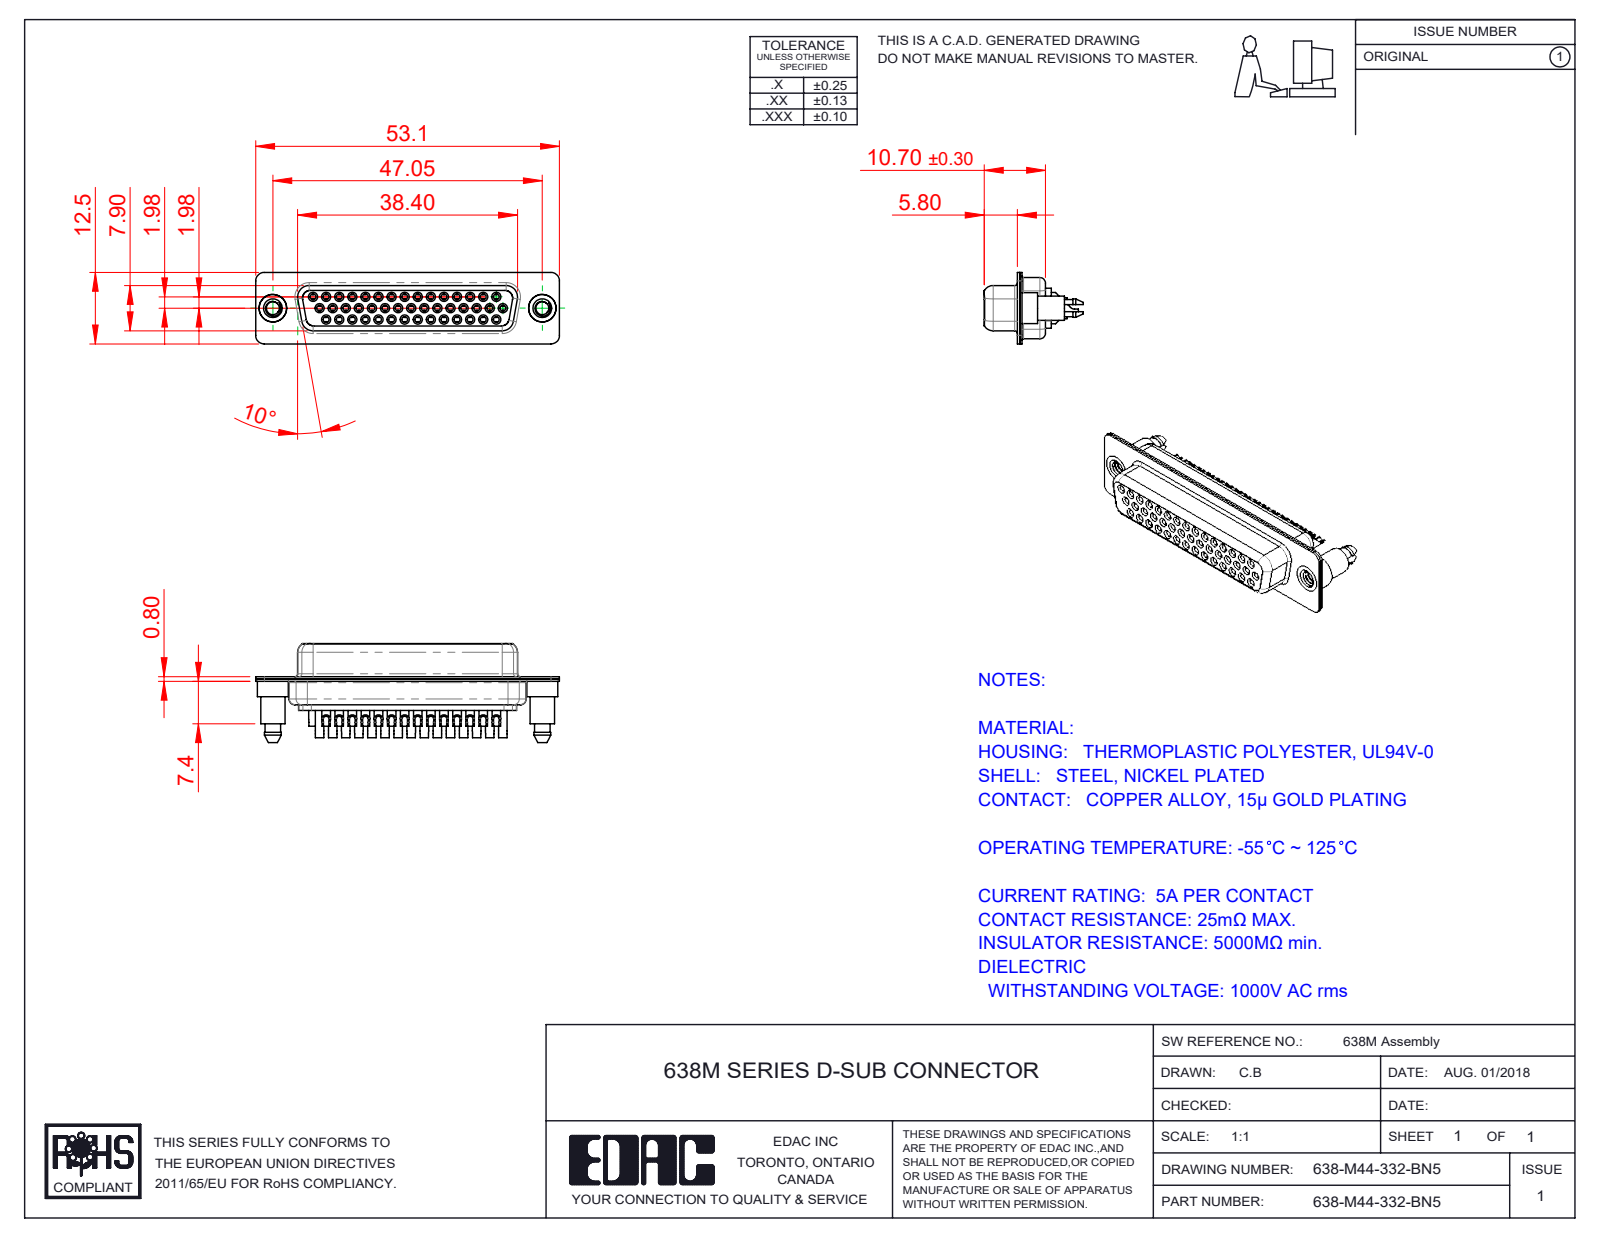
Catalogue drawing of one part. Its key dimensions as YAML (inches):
part_name: "638-M44-332-BN5; 638M Shell Rear_44 Contacts; 638M 4-40 Threaded Boardlock; 638M Shell Front_44 Contacts (+4 more)"
step_written_by: "SolidWorks 2020 (CONFIG_CONTROL_DESIGN)"
units: inches
bodies: {solids: 49, faces: 2749, planar: 831, cylindrical: 1093, other: 825}
overall_size: [2.089, 0.681, 0.492]
volume: 0.228
surface_area: 19.62
round_holes:
  - {diameter: 0.039, count: 44}
  - {diameter: 0.043, count: 44}
  - {diameter: 0.067, count: 44}
  - {diameter: 0.071, count: 44}
  - {diameter: 0.079, count: 44}
  - {diameter: 0.089, count: 2}
  - {diameter: 0.157, count: 2}
  - {diameter: 0.189, count: 2}
round_bosses_or_shafts:
  - {diameter: 0.087, count: 44}
  - {diameter: 0.063, count: 44}
  - {diameter: 0.059, count: 44}
  - {diameter: 0.213, count: 2}
  - {diameter: 0.193, count: 2}
  - {diameter: 0.167, count: 2}
partial_cylinders:
  - {radius: 0.059, count: 18}
  - {radius: 0.079, count: 12}
  - {radius: 0.063, count: 10}
  - {radius: 0.053, count: 9}
  - {radius: 0.039, count: 7}
  - {radius: 0.01, count: 4}
  - {radius: 0.02, count: 4}
  - {radius: 0.024, count: 4}
face_to_face_distances: [0.016, 0.055, 0.018, 0.333, 0.35, 0.039, 0.071, 0.244, 0.278, 0.073]
hole_center_spacings: [0.09, 0.09, 0.156, 0.18, 0.324, 0.27, 0.45, 0.59]
